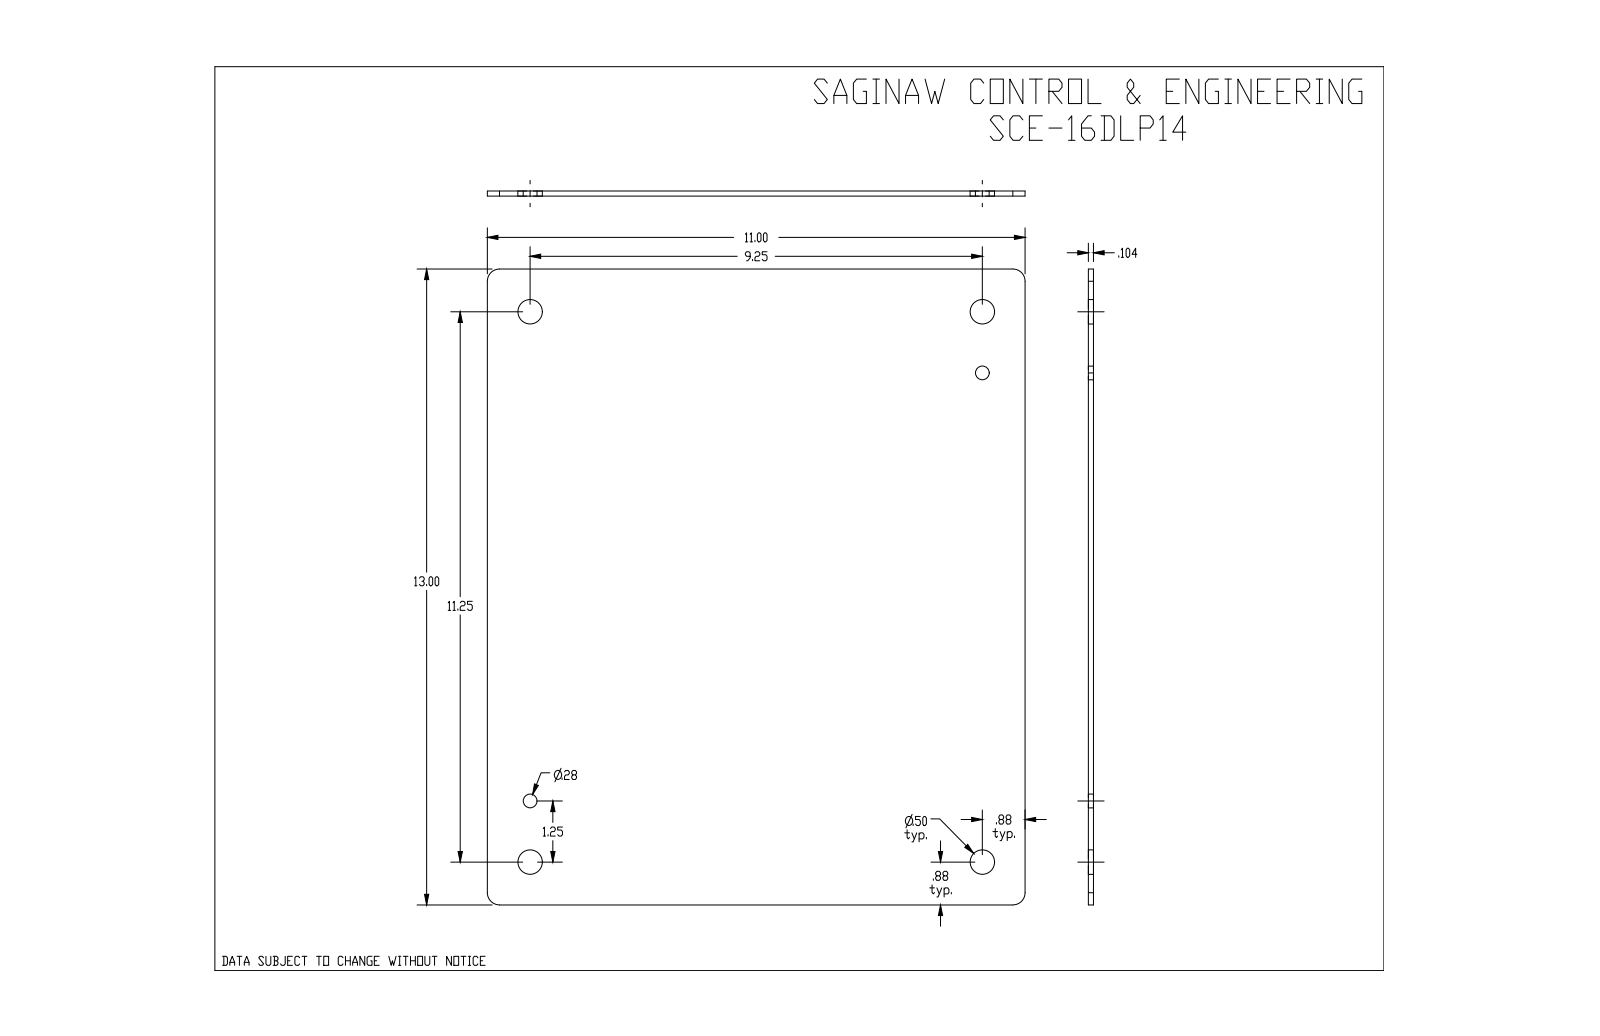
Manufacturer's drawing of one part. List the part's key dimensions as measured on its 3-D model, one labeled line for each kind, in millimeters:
Part name (STEP PRODUCT): SCE-16DLP14
STEP written by: SolidWorks 2019 (CONFIG_CONTROL_DESIGN)
Units: millimetres
Bodies: 1 solid, 16 faces (6 planar, 10 cylindrical, 0 other)
Overall size (bounding box): 330.2 × 279.4 × 2.6
Volume: 242 000 mm³ · Surface area: 187 000 mm²
Round holes (diameter × count): ⌀12.7 ×4, ⌀7.1 ×1, ⌀7.1 ×1
Partial cylindrical surfaces — rounded edges, fillets, slot ends (radius × count): R6.4 ×4
Main face-to-face distances: 2.6, 279.4, 330.2
Hole centre spacings: 31.8, 235, 237.1, 254, 285.8, 346, 370, 323.4
